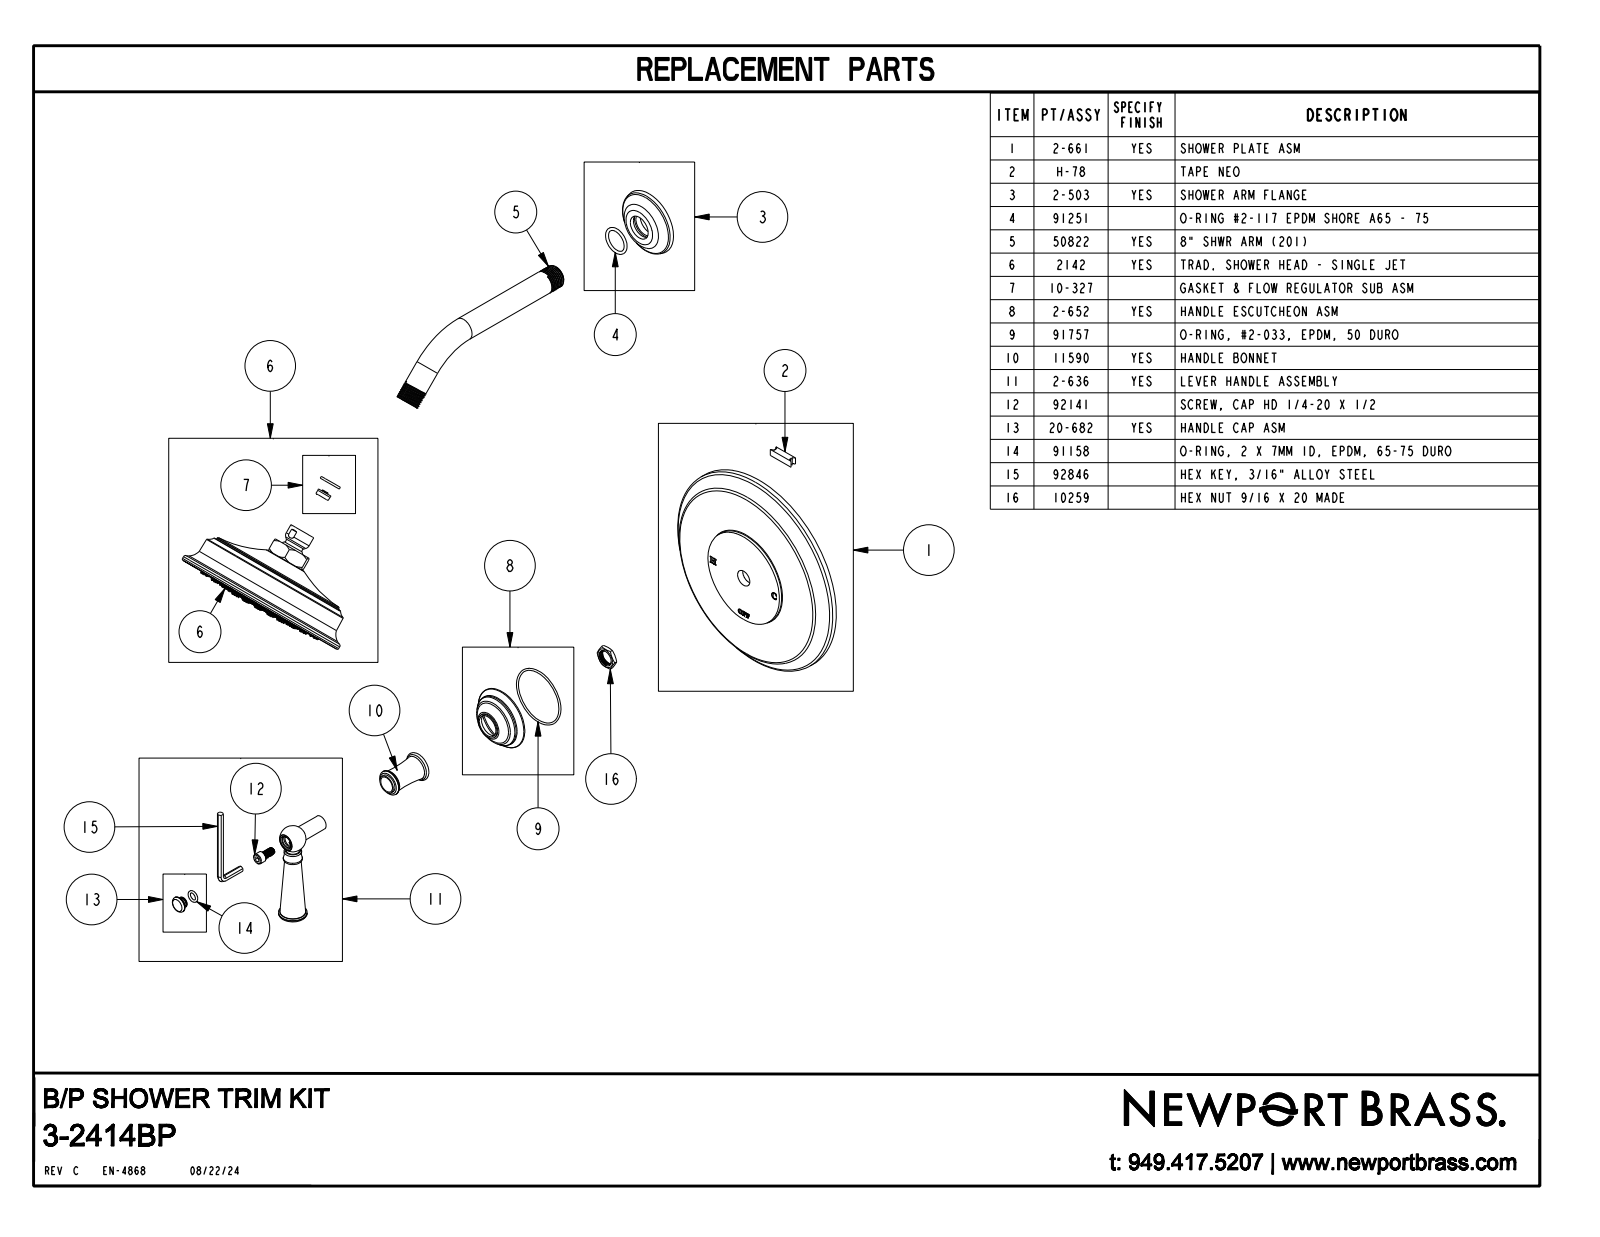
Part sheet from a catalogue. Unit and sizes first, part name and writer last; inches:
Units: inches
Overall size (bounding box): 16.935 × 10.691 × 7.5
Round holes (diameter × count): ⌀0.05 ×90, ⌀0.22 ×1, ⌀0.604 ×1, ⌀5.275 ×1
Round bosses / shafts (diameter × count): ⌀0.813 ×2, ⌀7.5 ×1, ⌀6.2 ×1, ⌀5.22 ×1, ⌀4.83 ×1, ⌀1.42 ×1, ⌀1.1 ×1, ⌀0.983 ×1
Main face-to-face distances: 0.625, 0.125, 0.75, 0.48, 0.145, 0.27, 1.014, 1.011, 2.025, 2.986
Hole centre spacings: 0.48, 1.84, 1.84, 2.27, 0.952, 1.408, 0.474, 2.24
Volume: 69.78 in³ · Surface area: 232.7 in²
Bodies: 2 solids, 1223 faces (269 planar, 228 cylindrical, 726 other)
Part name (STEP PRODUCT): 3-2414BP
STEP written by: CREO PARAMETRIC BY PTC INC, 2018400 (CONFIG_CONTROL_DESIGN)
